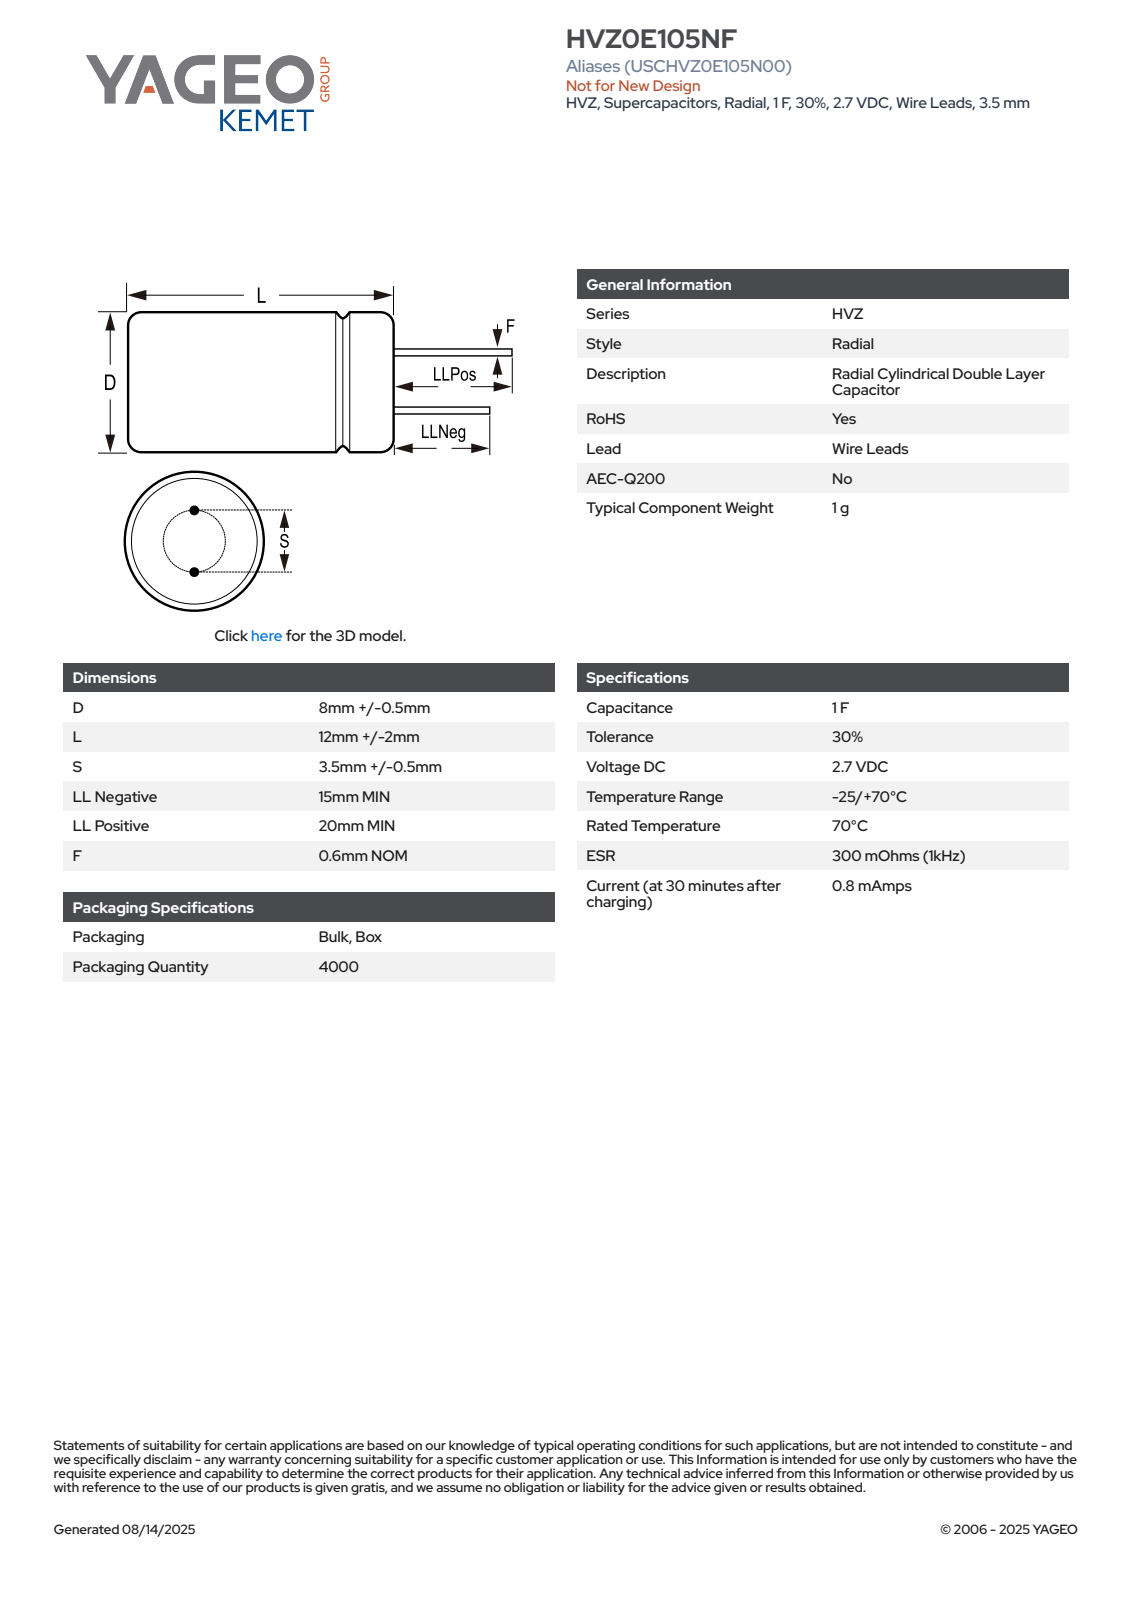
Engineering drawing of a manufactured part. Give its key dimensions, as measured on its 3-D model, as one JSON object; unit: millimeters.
{"part_name": "CDR_CCW_D8.5L14S3.5F0.6", "step_written_by": "SolidWorks 2014 (AUTOMOTIVE_DESIGN)", "units": "millimeters", "bodies": {"solids": 1, "faces": 82, "planar": 26, "cylindrical": 17, "other": 39}, "overall_size": [34, 8.51, 8.5], "volume_mm3": 797, "surface_area_mm2": 536, "round_bosses_or_shafts": [[0.6, 2], [8.5, 1]], "partial_cylinders_radius": [[4.26, 1]], "face_to_face_distances": [14, 34, 20, 29, 15, 5]}
